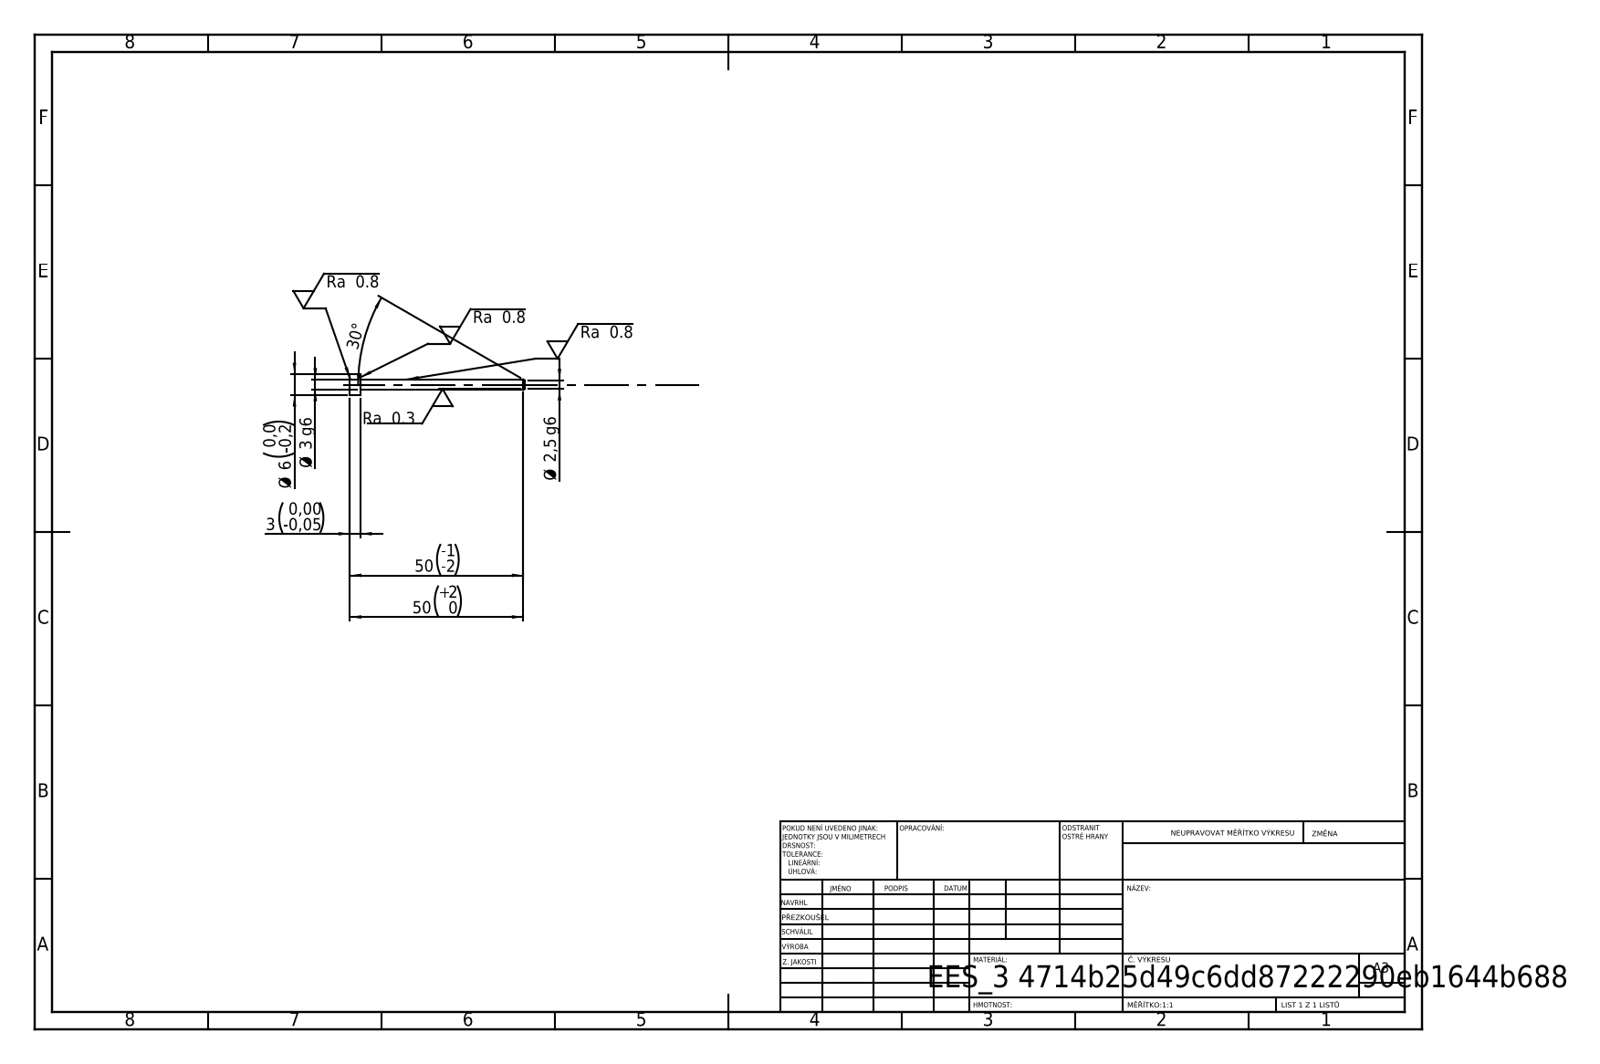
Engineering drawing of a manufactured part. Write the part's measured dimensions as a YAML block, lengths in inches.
step_written_by: "SolidWorks 2019 (CONFIG_CONTROL_DESIGN)"
units: inches
bodies: {solids: 1, faces: 11, planar: 3, cylindrical: 6, other: 2}
overall_size: [1.985, 0.236, 0.236]
volume: 0.026
surface_area: 0.871
round_holes:
  - {diameter: 0.098, count: 1}
round_bosses_or_shafts:
  - {diameter: 0.236, count: 1}
  - {diameter: 0.118, count: 1}
face_to_face_distances: [0.118, 1.85, 1.969]
